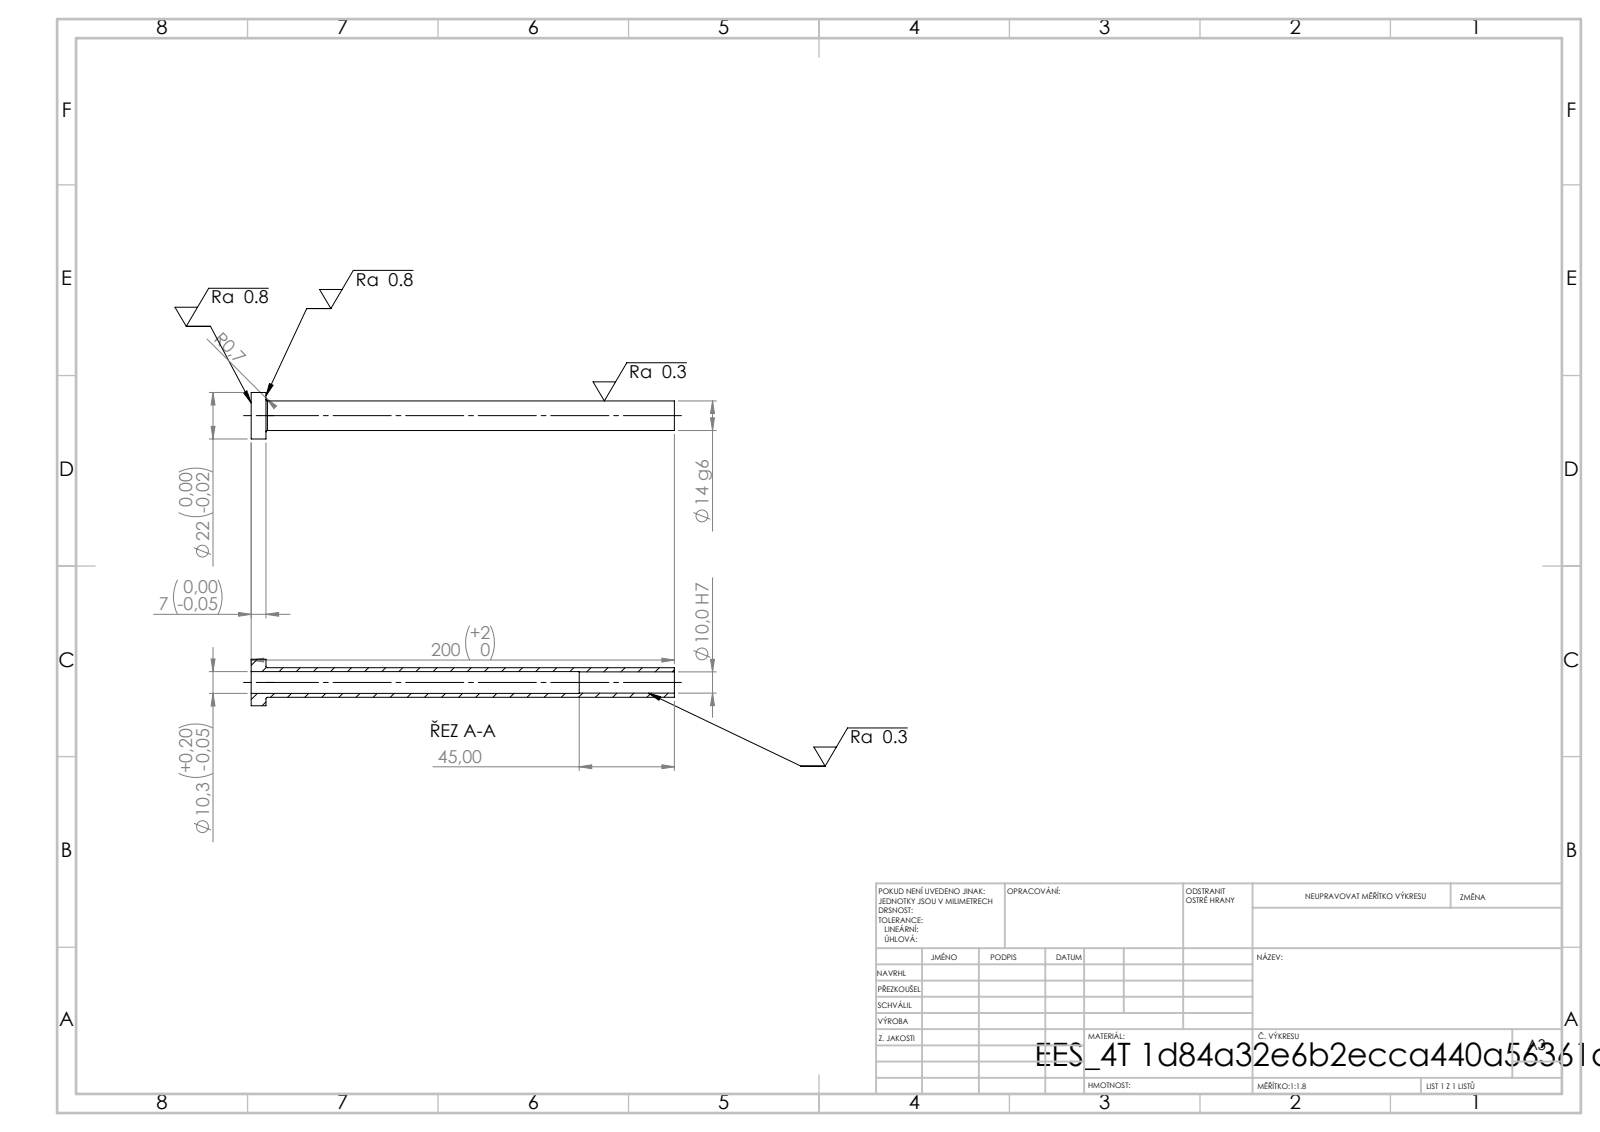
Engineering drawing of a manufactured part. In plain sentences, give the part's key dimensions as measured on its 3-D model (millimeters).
Its 3-D file was written by "SolidWorks 2019 (CONFIG_CONTROL_DESIGN)". It is 1 solid with 14 faces: 4 planar, 8 cylindrical and 2 other. Overall it measures 200 by 22 by 22 millimeters. Its volume is 15 926 cubic millimeters and its surface area 15 992 square millimeters. Round holes: 1 of diameter 10, 1 of diameter 10.3. Round bosses or shafts: 1 of diameter 22, 1 of diameter 14. The main face-to-face distances are 7, 200, 193, 155, 148, 45.
